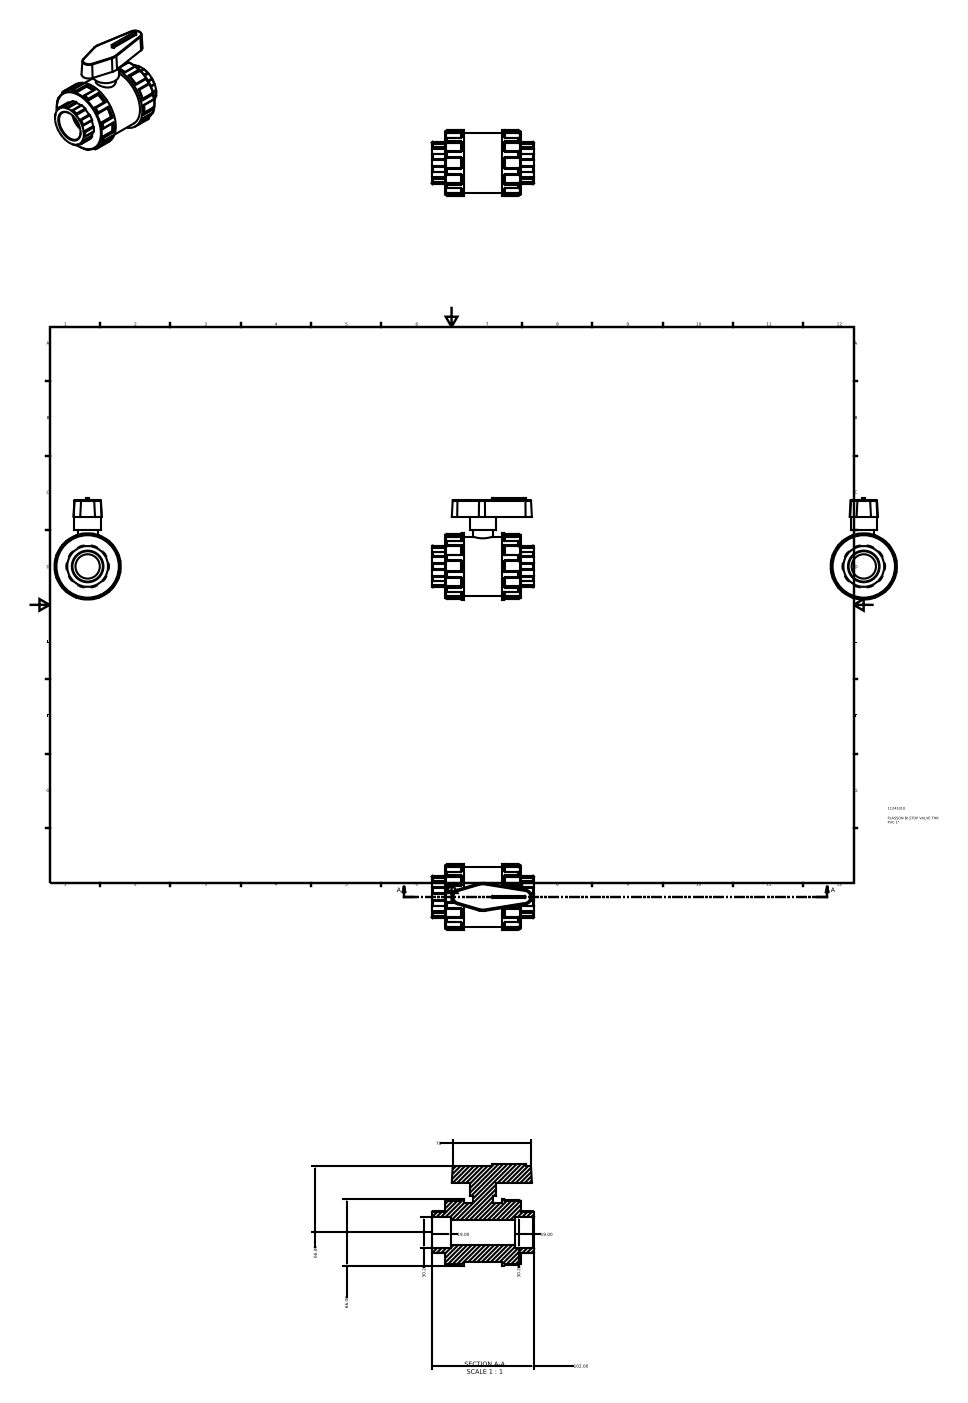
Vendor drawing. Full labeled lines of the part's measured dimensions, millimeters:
Part name (STEP PRODUCT): 11241010
STEP written by: Autodesk Inventor 2015 (AUTOMOTIVE_DESIGN)
Units: millimetres
Bodies: 1 solid, 434 faces (114 planar, 192 cylindrical, 128 other)
Overall size (bounding box): 102 × 100.98 × 66
Volume: 241 849 mm³ · Surface area: 41 387 mm²
Round holes (diameter × count): ⌀24.23 ×1, ⌀30.29 ×1
Round bosses / shafts (diameter × count): ⌀66 ×1, ⌀63.36 ×1, ⌀59.4 ×1, ⌀26.4 ×1, ⌀19.8 ×1
Partial cylindrical surfaces — rounded edges, fillets, slot ends (radius × count): R0.91 ×68, R0.61 ×4, R1.32 ×2, R20.3 ×1, R21.2 ×1
Main face-to-face distances: 19, 75.4, 13.3, 69.7, 56.4, 16.5, 32.3, 88.7, 37.4, 83
